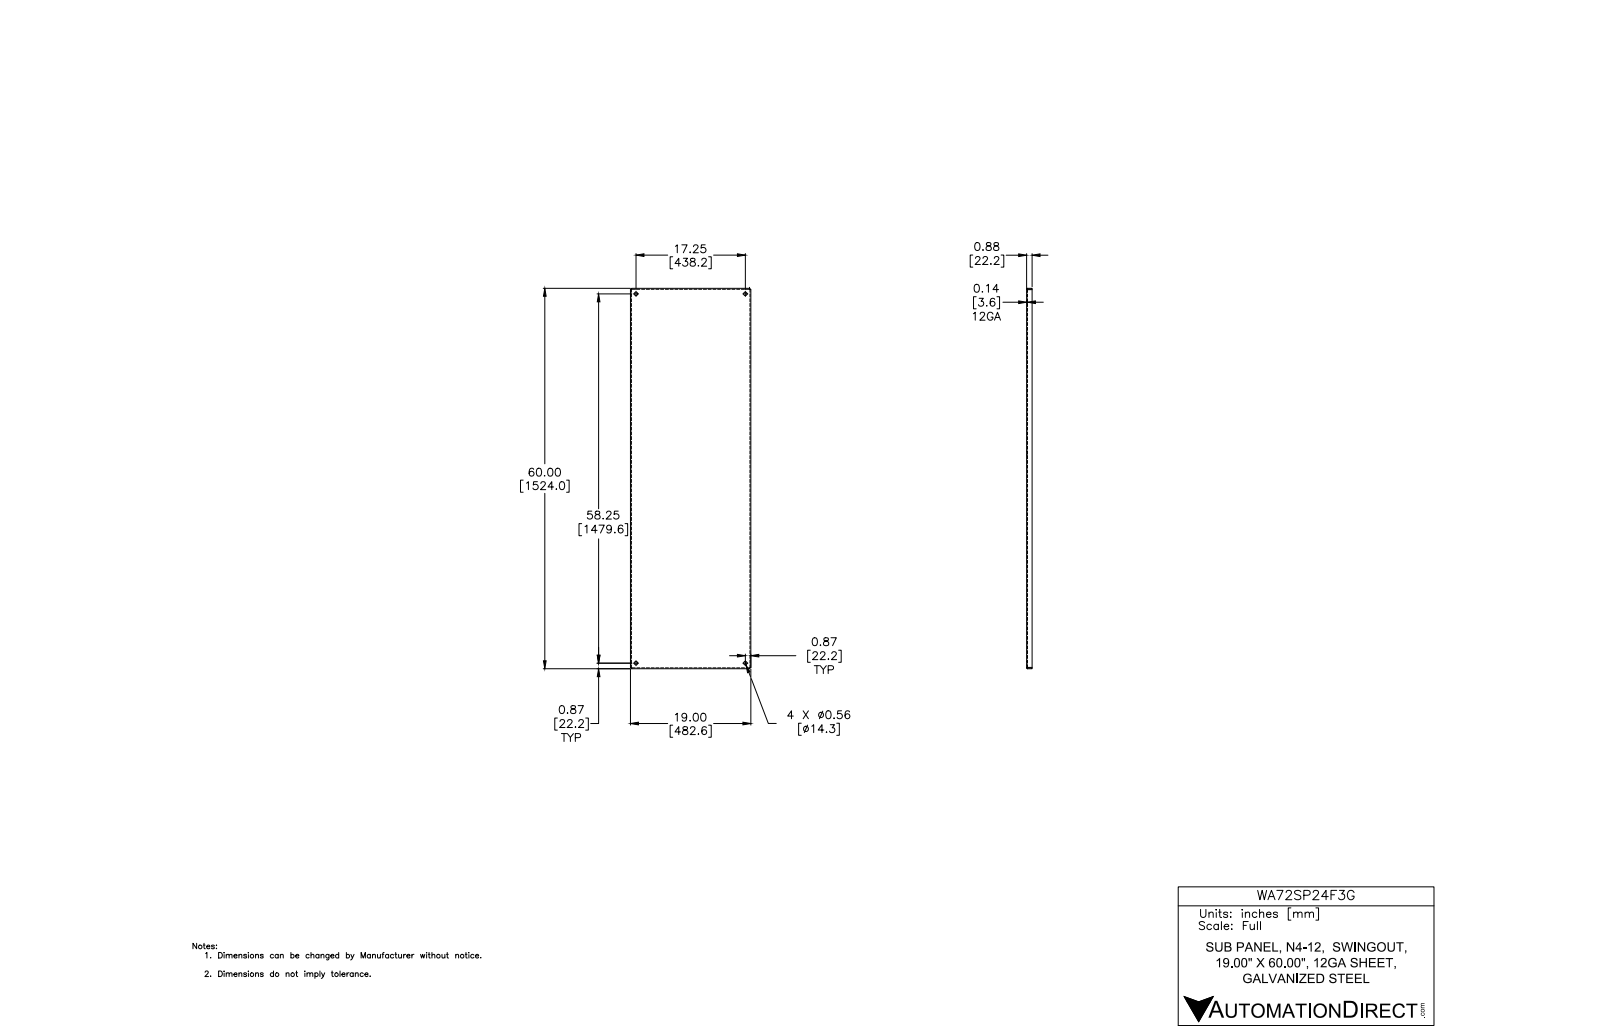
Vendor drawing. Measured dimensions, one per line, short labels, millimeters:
name: WA60SP24F3G-WA90SP36F4G
written by: Autodesk Inventor 2012 (AUTOMOTIVE_DESIGN)
unit: mm
bodies: 1 solid, 42 faces (22 planar, 12 cylindrical, 8 other)
size: 1524 × 482.6 × 22.2
volume: 1 930 000 mm³; area: 1 631 000 mm²
holes: 4× ⌀14.3
rounds: 4× R0.8, 4× R3.2
face distances: 2.4, 480.2, 482.6, 477.9, 1521.6, 19.8, 22.2, 1524, 1519.3, 4.1
hole spacings: 438.2, 1479.6, 1543.1
